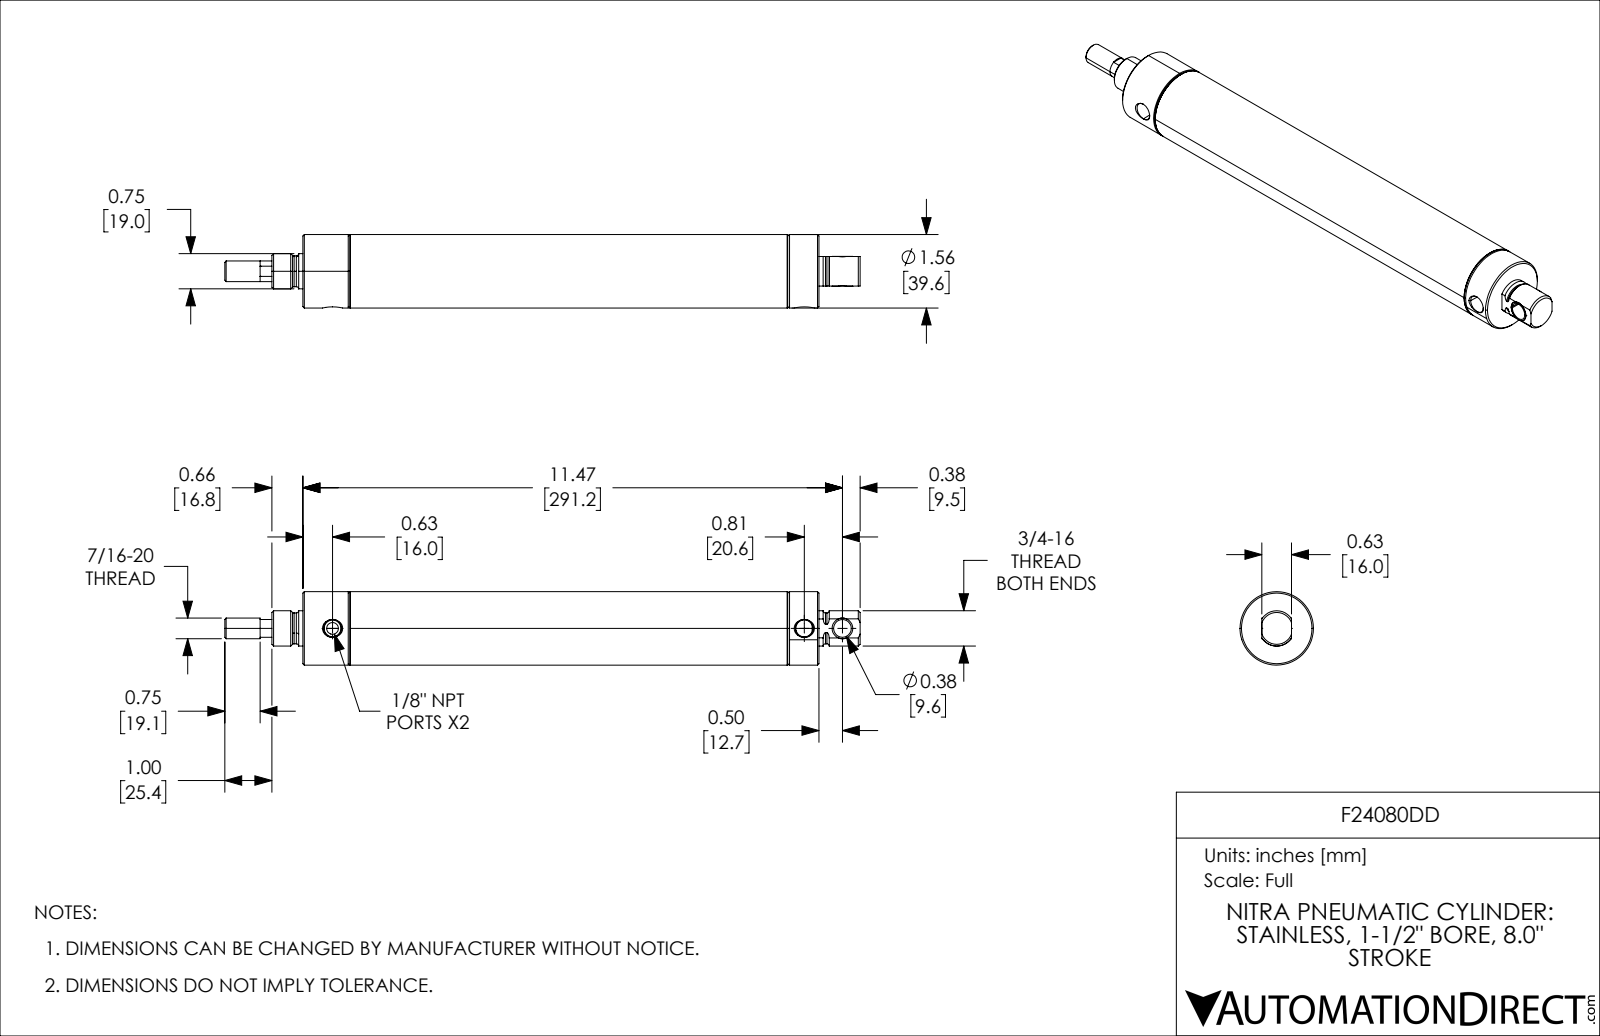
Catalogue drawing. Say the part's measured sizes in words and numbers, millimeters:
The part is named "F24080DD_9; F24080DD_5; F24080DD_7; F24080DD (+2 more)". Its 3-D file was written by "SolidWorks 2021 (CONFIG_CONTROL_DESIGN)". It is 5 solids with 157 faces: 35 planar, 58 cylindrical and 64 other. Overall it measures 342.9 by 39.62 by 39.62 millimeters. Its volume is 130 704 cubic millimeters and its surface area 92 517 square millimeters. Round holes: 1 of diameter 6.35, 1 of diameter 9.14, 1 of diameter 9.55, 1 of diameter 11.15, 1 of diameter 11.73, 1 of diameter 13.51, 1 of diameter 26.97, 1 of diameter 36.36. Round bosses or shafts: 1 of diameter 39.62, 1 of diameter 38.39, 1 of diameter 19.05, 1 of diameter 18.99, 1 of diameter 16.61, 1 of diameter 16.6, 1 of diameter 11.13, 1 of diameter 11.11. The main face-to-face distances are 22.22, 44.45, 203.2, 225.42, 247.65, 22.23, 30.86, 234.06, 256.28, 278.51. The hole center spacings are 20.57, 254.64, 275.21.
